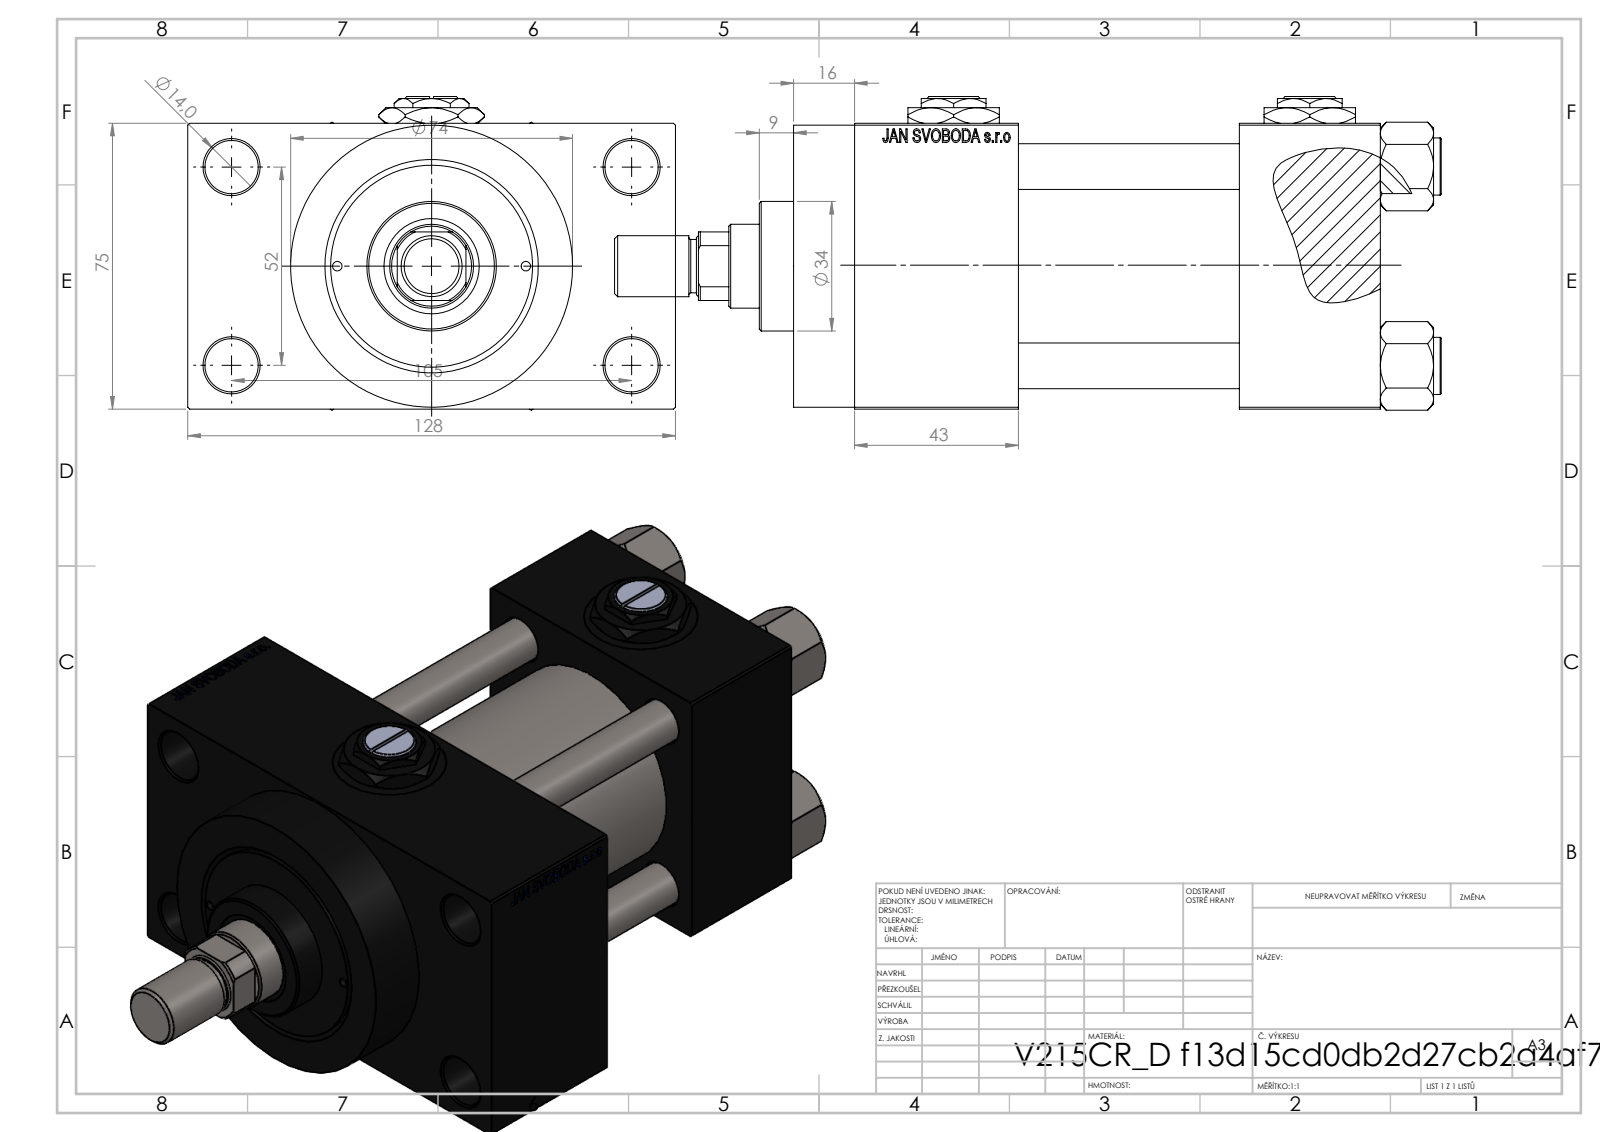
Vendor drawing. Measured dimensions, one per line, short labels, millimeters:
name: Zatka_pro_OIL_PORT; V215_VC_A; V215CR_D_Body; NUT_M5_D (+3 more)
written by: SolidWorks 2019 (CONFIG_CONTROL_DESIGN)
unit: mm
bodies: 14 solids, 1227 faces (551 planar, 108 cylindrical, 568 other)
size: 217 × 128 × 82.27
volume: 806 247 mm³; area: 170 659 mm²
holes: 4× ⌀12, 4× ⌀14, 2× ⌀2.5, 2× ⌀7, 2× ⌀20.96, 2× ⌀30, 1× ⌀10.5, 1× ⌀22, 1× ⌀25, 1× ⌀41, 1× ⌀50, 1× ⌀53
bosses: 4× ⌀15, 1× ⌀74, 1× ⌀56, 1× ⌀34, 1× ⌀16, 1× ⌀14
rounds: 1× R10.5
face distances: 75, 58, 37, 95, 26.5, 101.5, 101, 138, 43, 16
hole spacings: 26.19, 26.35, 36.98, 38.03, 52.3, 57.22, 58.43, 58.59
